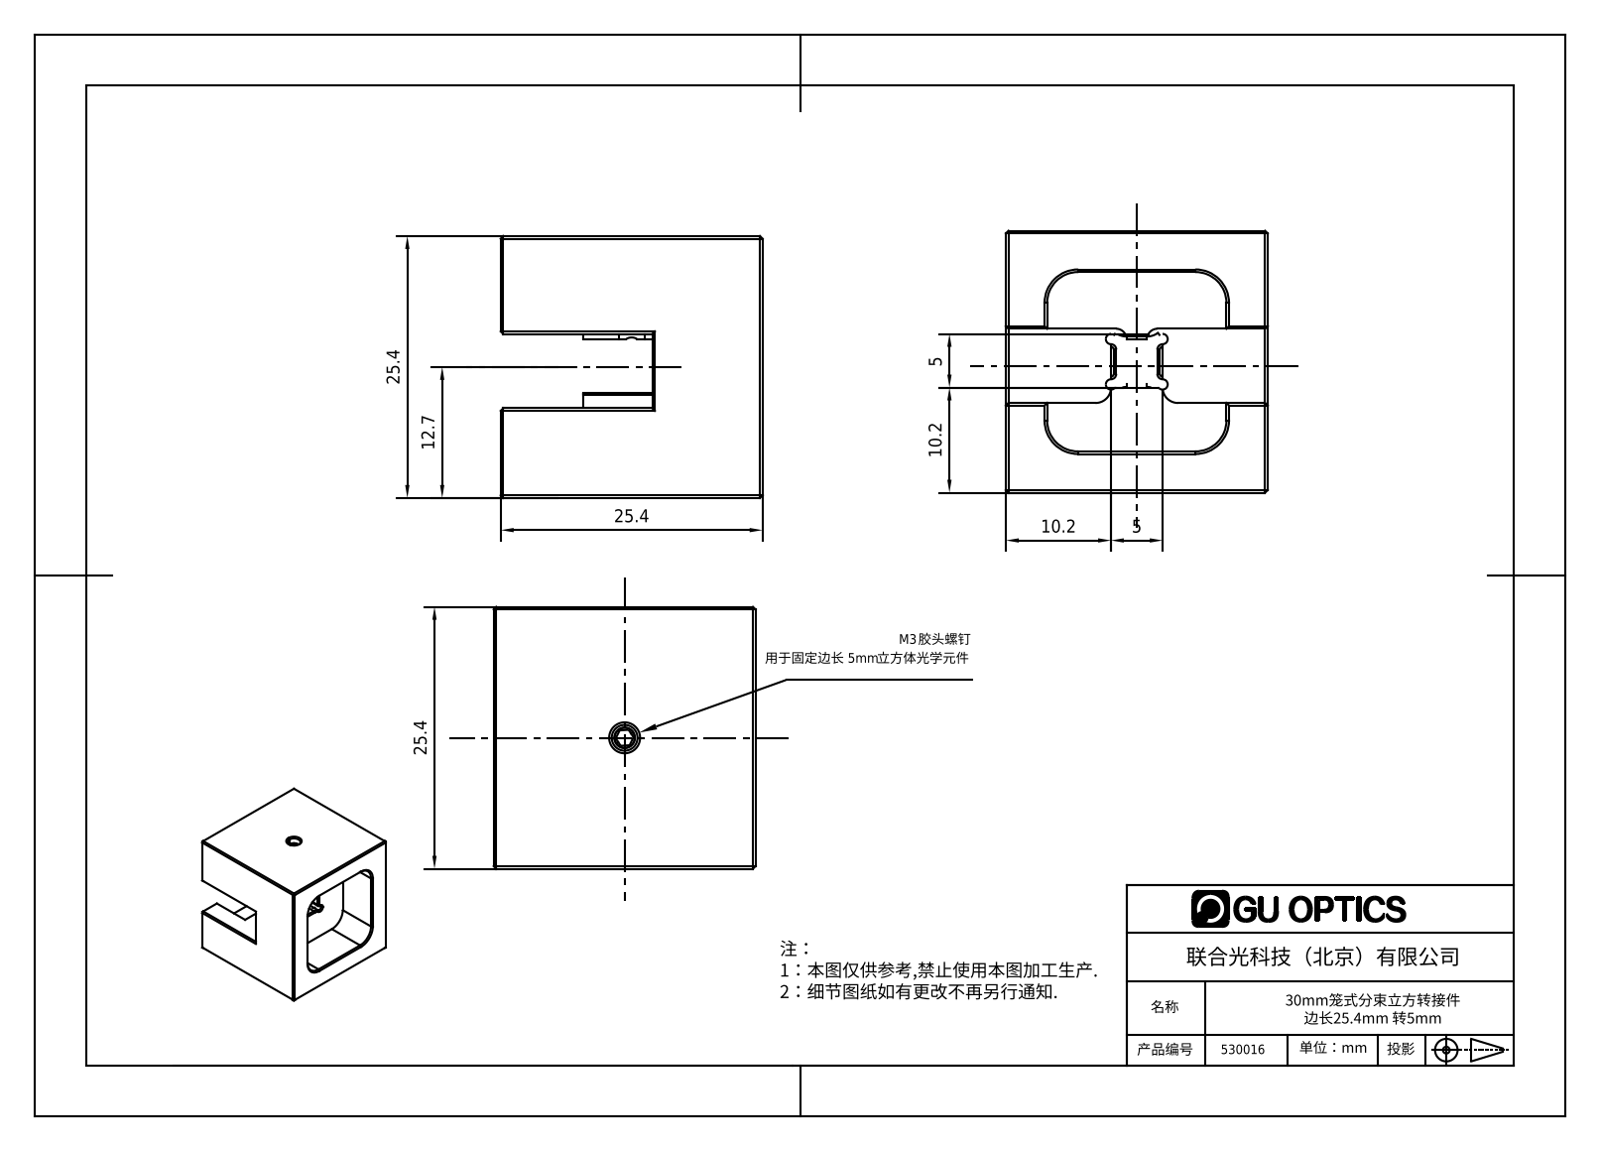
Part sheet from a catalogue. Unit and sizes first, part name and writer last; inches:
Units: inches
Overall size (bounding box): 1 × 1 × 1
Round holes (diameter × count): ⌀0.098 ×1
Partial cylindrical surfaces — rounded edges, fillets, slot ends (radius × count): R0.02 ×8, R0.079 ×4, R0.118 ×4, R0.039 ×2, R0.059 ×2
Main face-to-face distances: 1, 0.685, 0.157, 0.843, 0.315, 0.626, 0.374, 0.37, 0.469, 0.217
Bodies: 0 solids, 144 faces (90 planar, 28 cylindrical, 26 other)
Part name (STEP PRODUCT): 1.6.4.48_ZSJ-1F5_分束镜安装座转接件，边长25.4mm(1.0英寸)转5mm
STEP written by: SolidWorks 2018 (AUTOMOTIVE_DESIGN)
